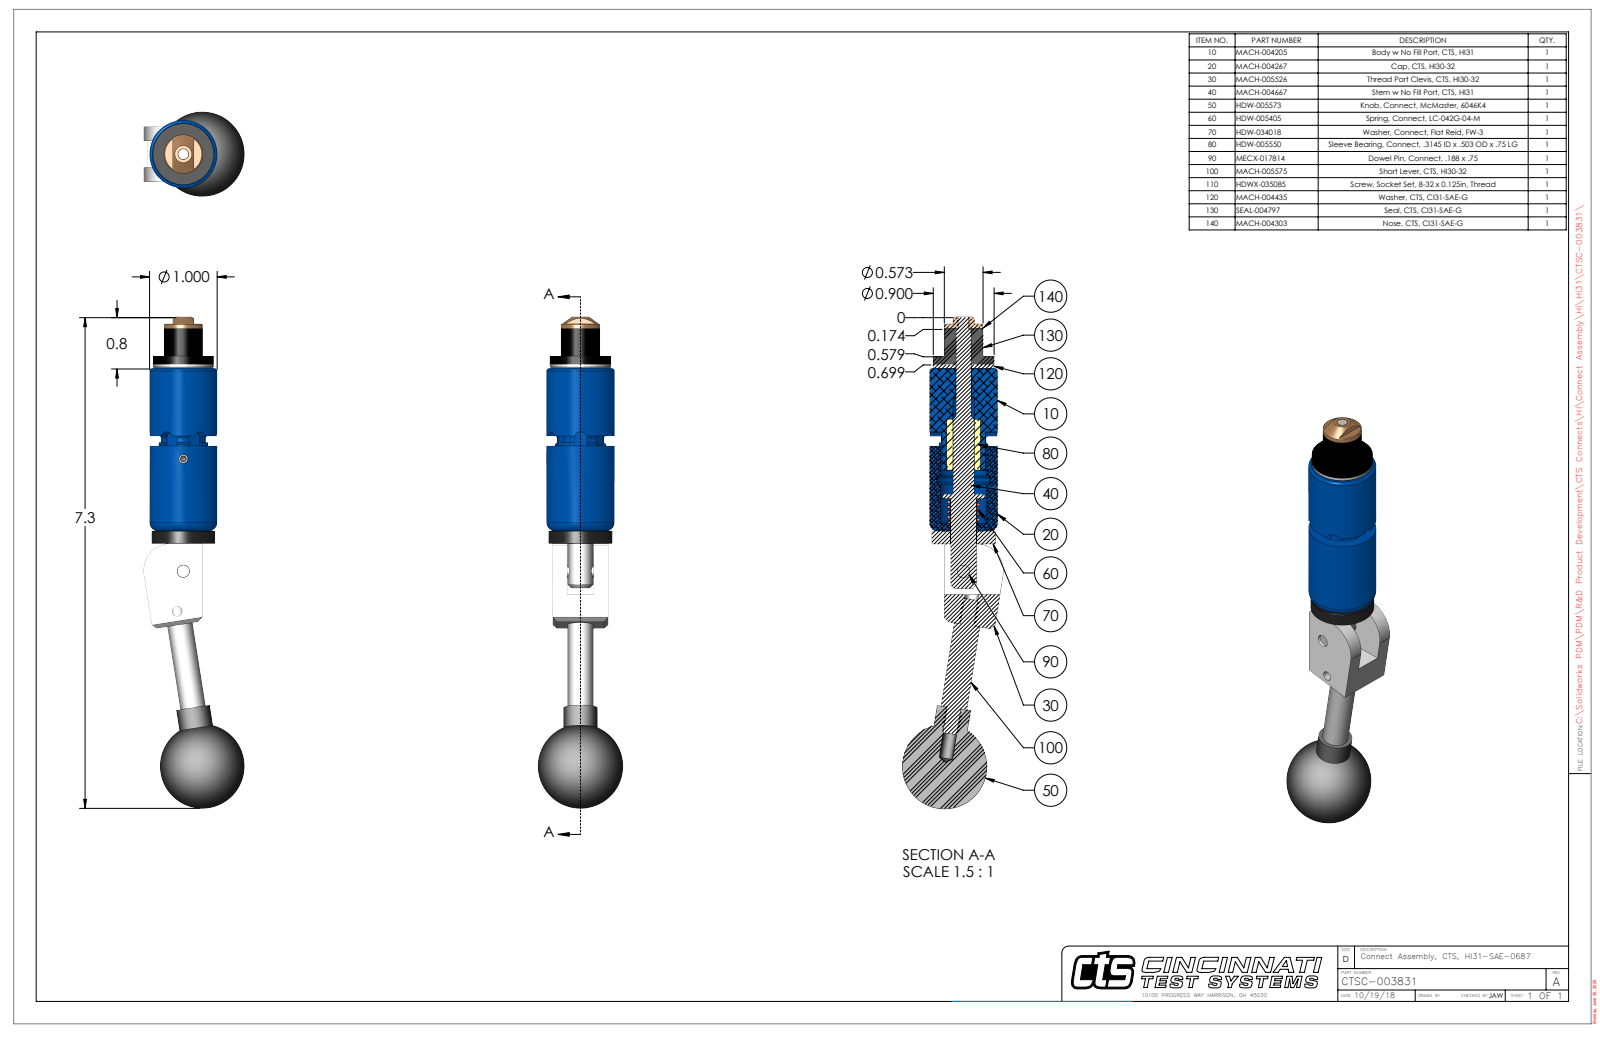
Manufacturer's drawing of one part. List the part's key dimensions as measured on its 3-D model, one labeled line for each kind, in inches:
Part name (STEP PRODUCT): CTSC-003831
STEP written by: SolidWorks 2023 (AUTOMOTIVE_DESIGN)
Units: inches
Bodies: 9 solids, 268 faces (101 planar, 109 cylindrical, 58 other)
Overall size (bounding box): 7.256 × 1.492 × 1.25
Volume: 3.989 in³ · Surface area: 33.38 in²
Round holes (diameter × count): ⌀0.201 ×2, ⌀0.136 ×1, ⌀0.15 ×1, ⌀0.159 ×1, ⌀0.189 ×1, ⌀0.218 ×1, ⌀0.228 ×1, ⌀0.229 ×1, ⌀0.385 ×1, ⌀0.392 ×1, ⌀0.688 ×1
Round bosses / shafts (diameter × count): ⌀1 ×1, ⌀0.936 ×1, ⌀0.9 ×1, ⌀0.573 ×1, ⌀0.5 ×1, ⌀0.38 ×1, ⌀0.375 ×1, ⌀0.25 ×1
Partial cylindrical surfaces — rounded edges, fillets, slot ends (radius × count): R0.093 ×6, R0.029 ×2, R0.375 ×1, R0.4 ×1, R0.455 ×1
Main face-to-face distances: 0.21, 0.602, 0.06, 2.46, 2.4, 0.812, 2.647, 2.587, 0.187, 0.391
Hole centre spacings: 0.599, 1.658, 2.252
